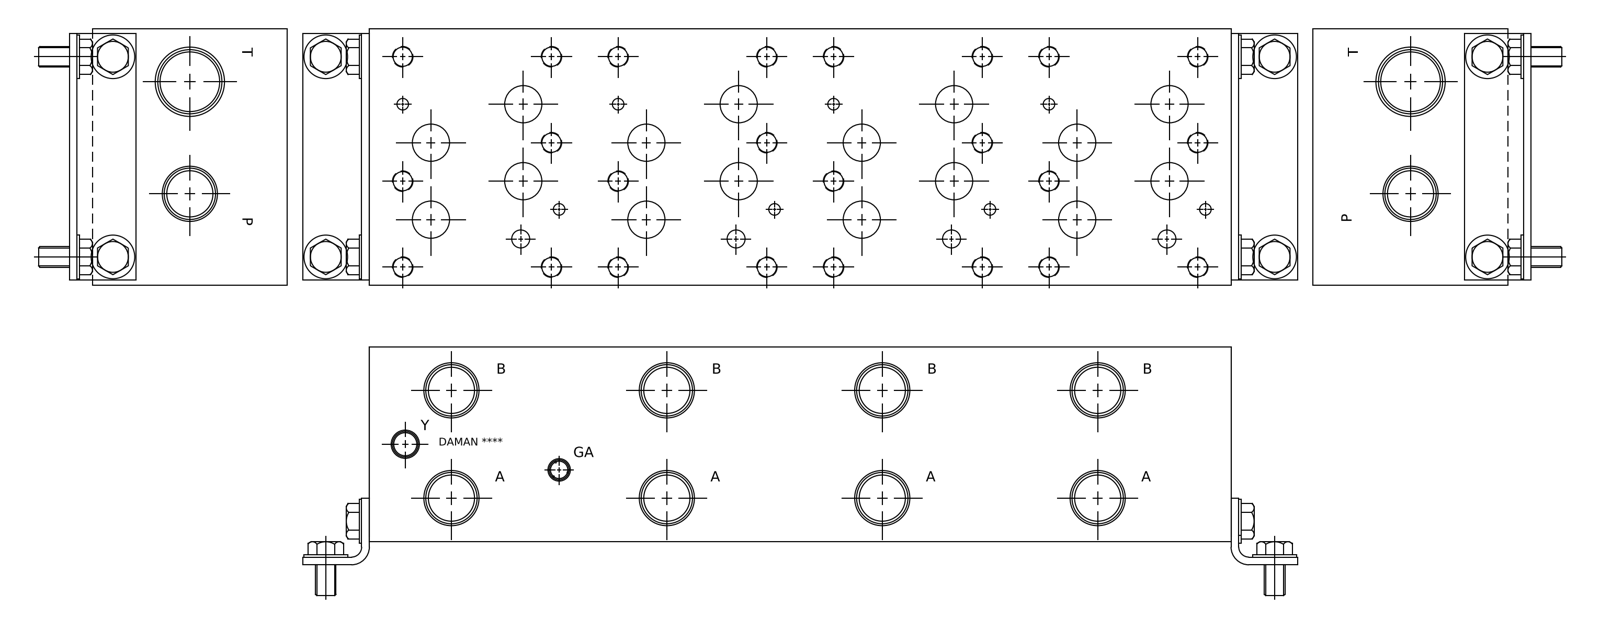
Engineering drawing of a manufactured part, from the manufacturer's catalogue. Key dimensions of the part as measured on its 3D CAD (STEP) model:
Part name (STEP PRODUCT): Part_AD08P045P_3D
STEP written by: Autodesk Inventor 2019 (AUTOMOTIVE_DESIGN)
Units: millimetres
Bodies: 1 solid, 800 faces (436 planar, 116 cylindrical, 248 other)
Overall size (bounding box): 533.4 × 158.75 × 120.65
Volume: 9 704 000 mm³ · Surface area: 422 951 mm²
Round holes (diameter × count): ⌀10.72 ×27, ⌀12.7 ×26, ⌀23.01 ×15, ⌀28.57 ×9, ⌀33.71 ×9, ⌀7.14 ×8, ⌀11.13 ×3, ⌀11.11 ×1, ⌀13.87 ×1, ⌀14.3 ×1, ⌀17.3 ×1, ⌀23.02 ×1
Main face-to-face distances: 120.65, 158.75, 533.4, 19, 139.75, 90.42, 30.23, 19.51, 513.89, 514.4
Hole centre spacings: 133.35, 266.7, 191.98, 400.05, 61.92, 270.92, 79.84, 141.6
